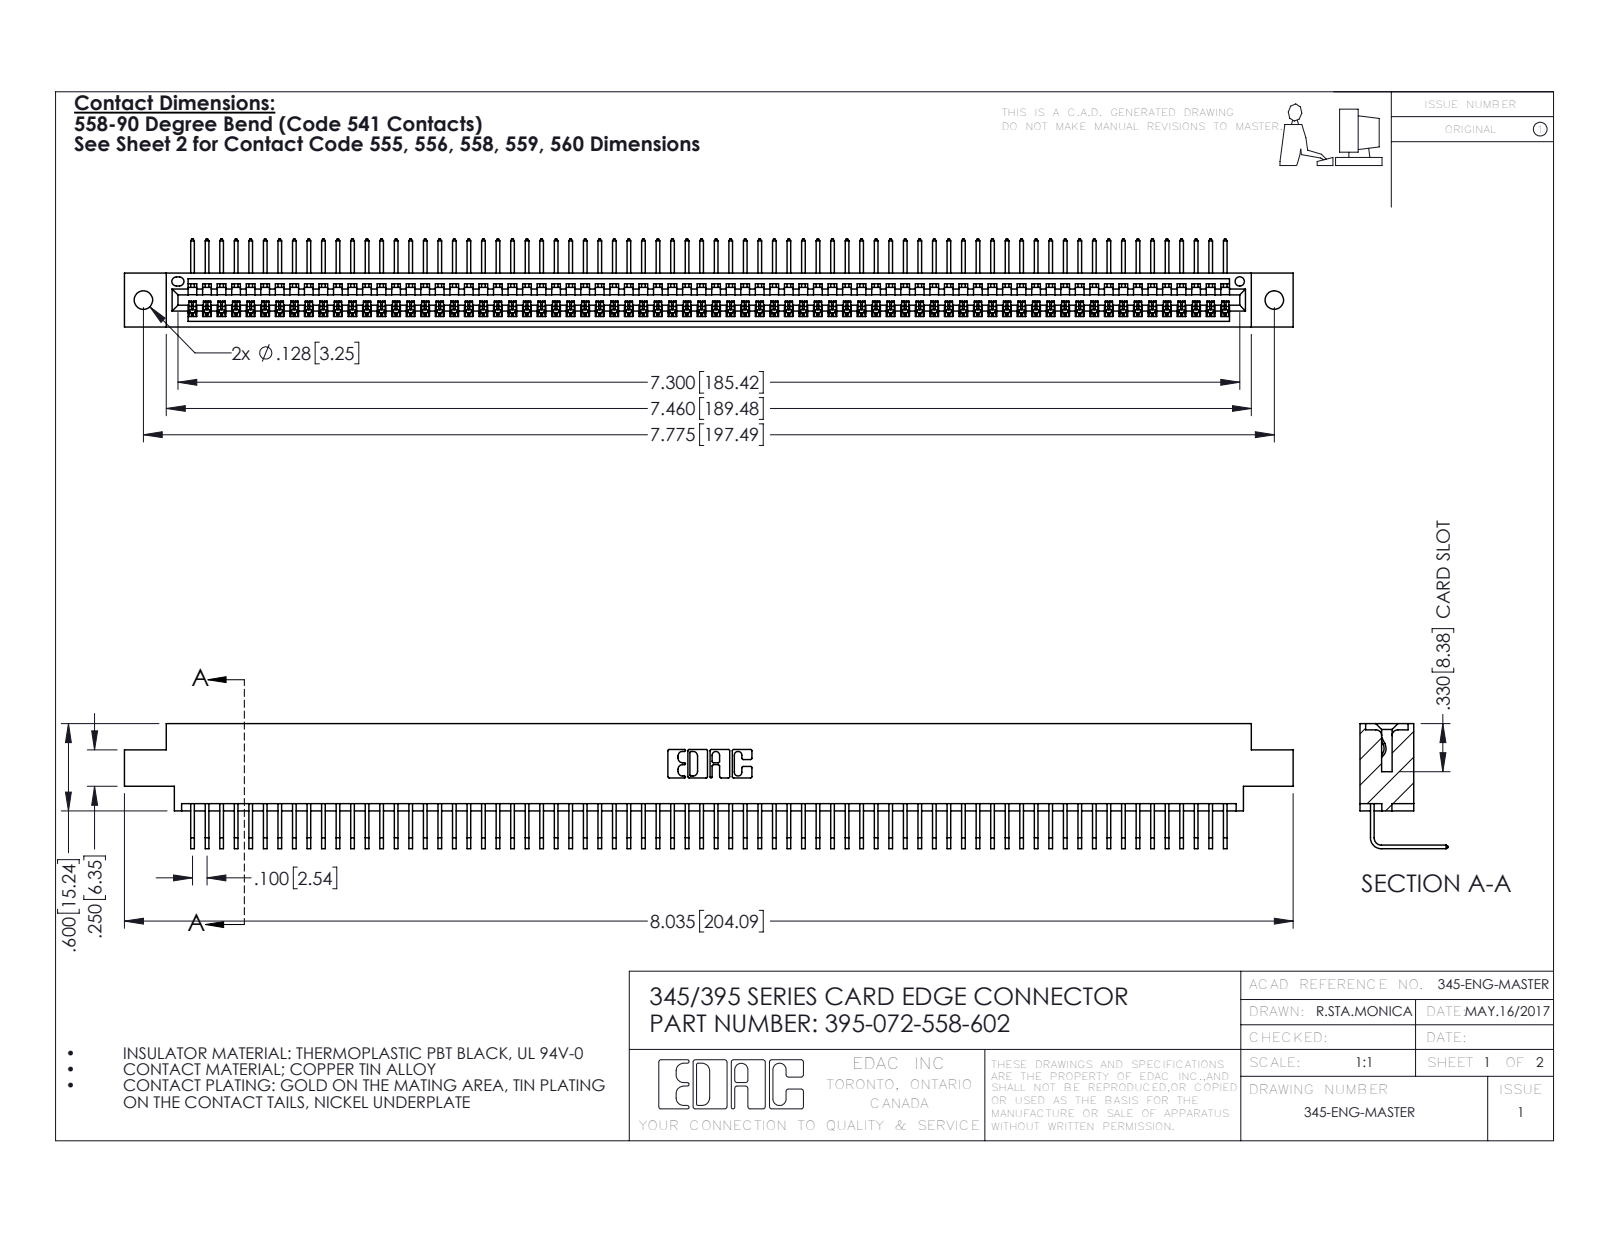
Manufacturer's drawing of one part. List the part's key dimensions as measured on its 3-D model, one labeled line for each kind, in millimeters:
Part name (STEP PRODUCT): 345 Part_0.170 Offset - 0.128 Dia; 395-072-558-602; 345-292-001_558 Tail - 2
STEP written by: SolidWorks 2016 (CONFIG_CONTROL_DESIGN)
Units: millimetres
Bodies: 73 solids, 4450 faces (3108 planar, 1342 cylindrical, 0 other)
Overall size (bounding box): 204.1 × 21.8 × 15.4
Volume: 19 710 mm³ · Surface area: 27 880 mm²
Round holes (diameter × count): ⌀3.3 ×2, ⌀1.6 ×1
Partial cylindrical surfaces — rounded edges, fillets, slot ends (radius × count): R0.2 ×144, R0.3 ×22, R0.2 ×6, R0.8 ×6, R0.7 ×3, R0.8 ×2, R1 ×2, R0.4 ×1
Main face-to-face distances: 1.8, 7.6, 9.4, 5.1, 2.5, 6.9, 0.6, 5.7, 4.4, 3.8
Hole centre spacings: 6.9, 191.5, 197.5
